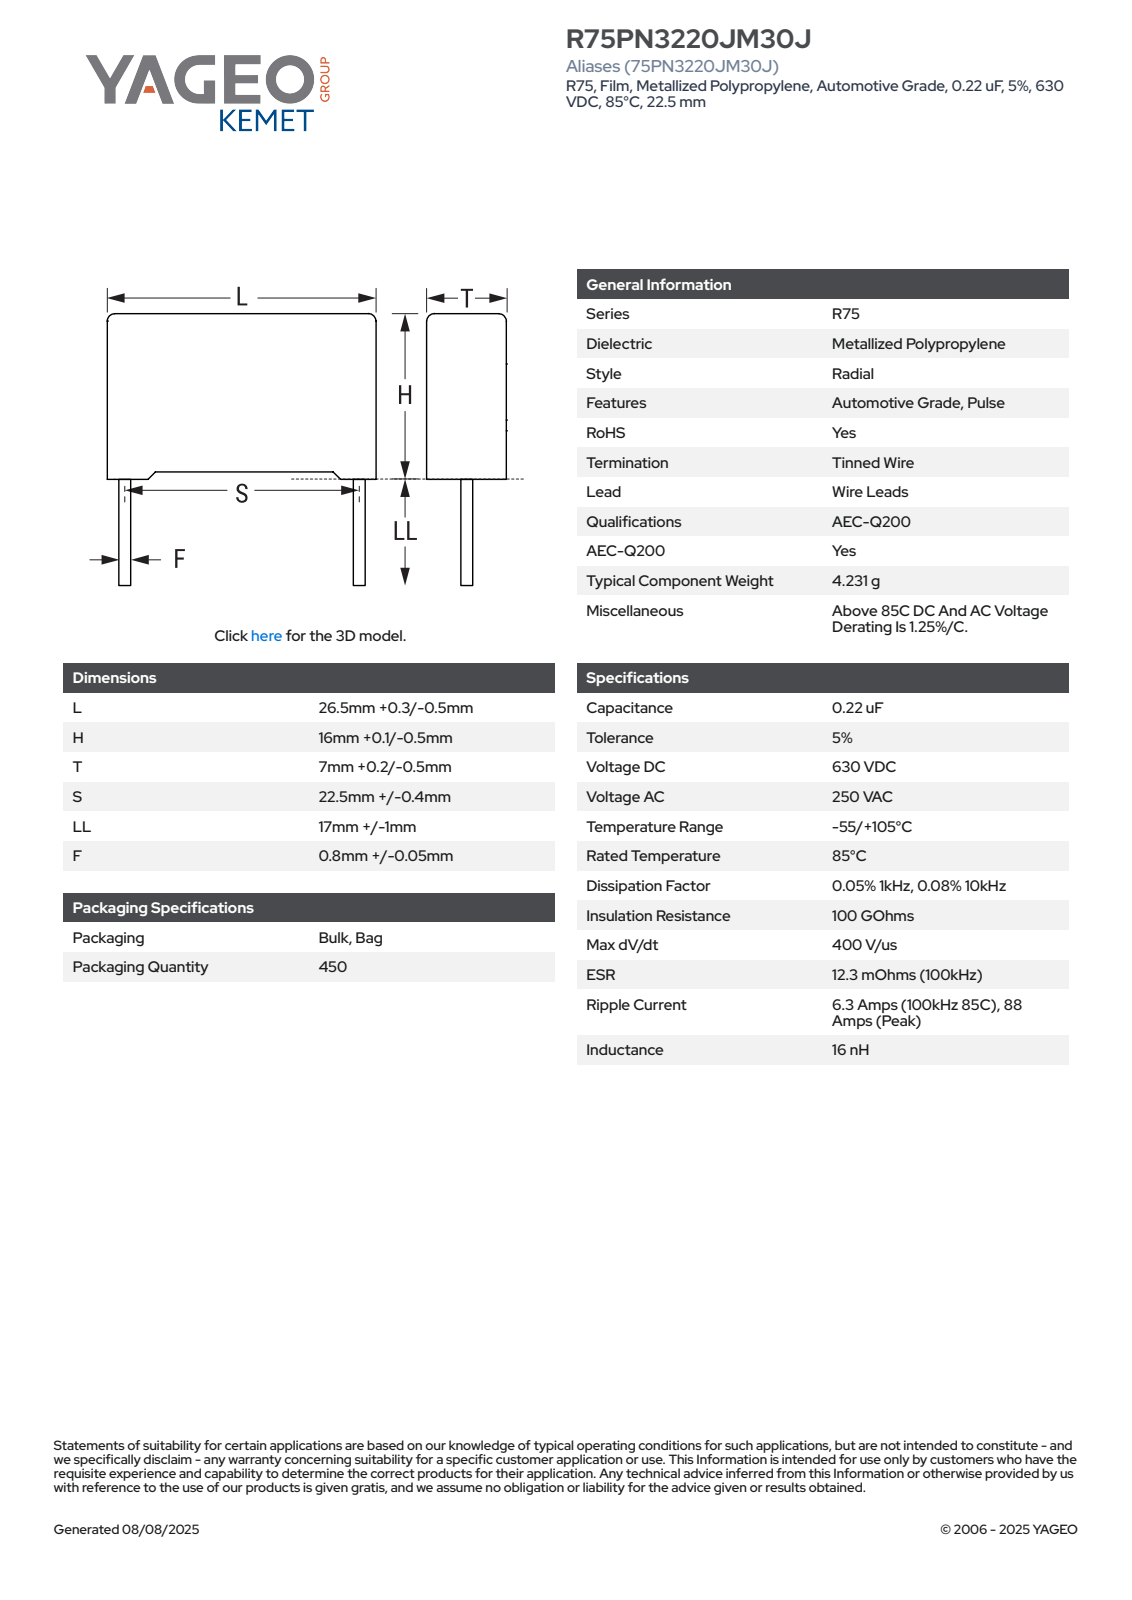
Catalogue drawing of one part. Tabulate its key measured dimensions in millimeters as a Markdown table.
| quantity | value |
| --- | --- |
| part name | CFR_RB2_26.5X16X7_L26.8H16.1T7.2S22.5LL18F0.85 |
| STEP written by | SolidWorks 2021 (AUTOMOTIVE_DESIGN) |
| units | millimeters |
| bodies | 4 solids, 85 faces (77 planar, 8 cylindrical, 0 other) |
| overall size | 34.1 × 26.8 × 7.21 |
| volume | 3 004 mm³ |
| surface area | 1 625 mm² |
| round bosses / shafts (diameter × count) | 0.85 × 2 |
| partial cylindrical surfaces (radius × count) | 0.5 × 4 |
| main face-to-face distances | 7.2, 15.35, 26.8, 15.54, 0.89, 0.56, 0.75, 16.1, 6.31, 5.42 |
